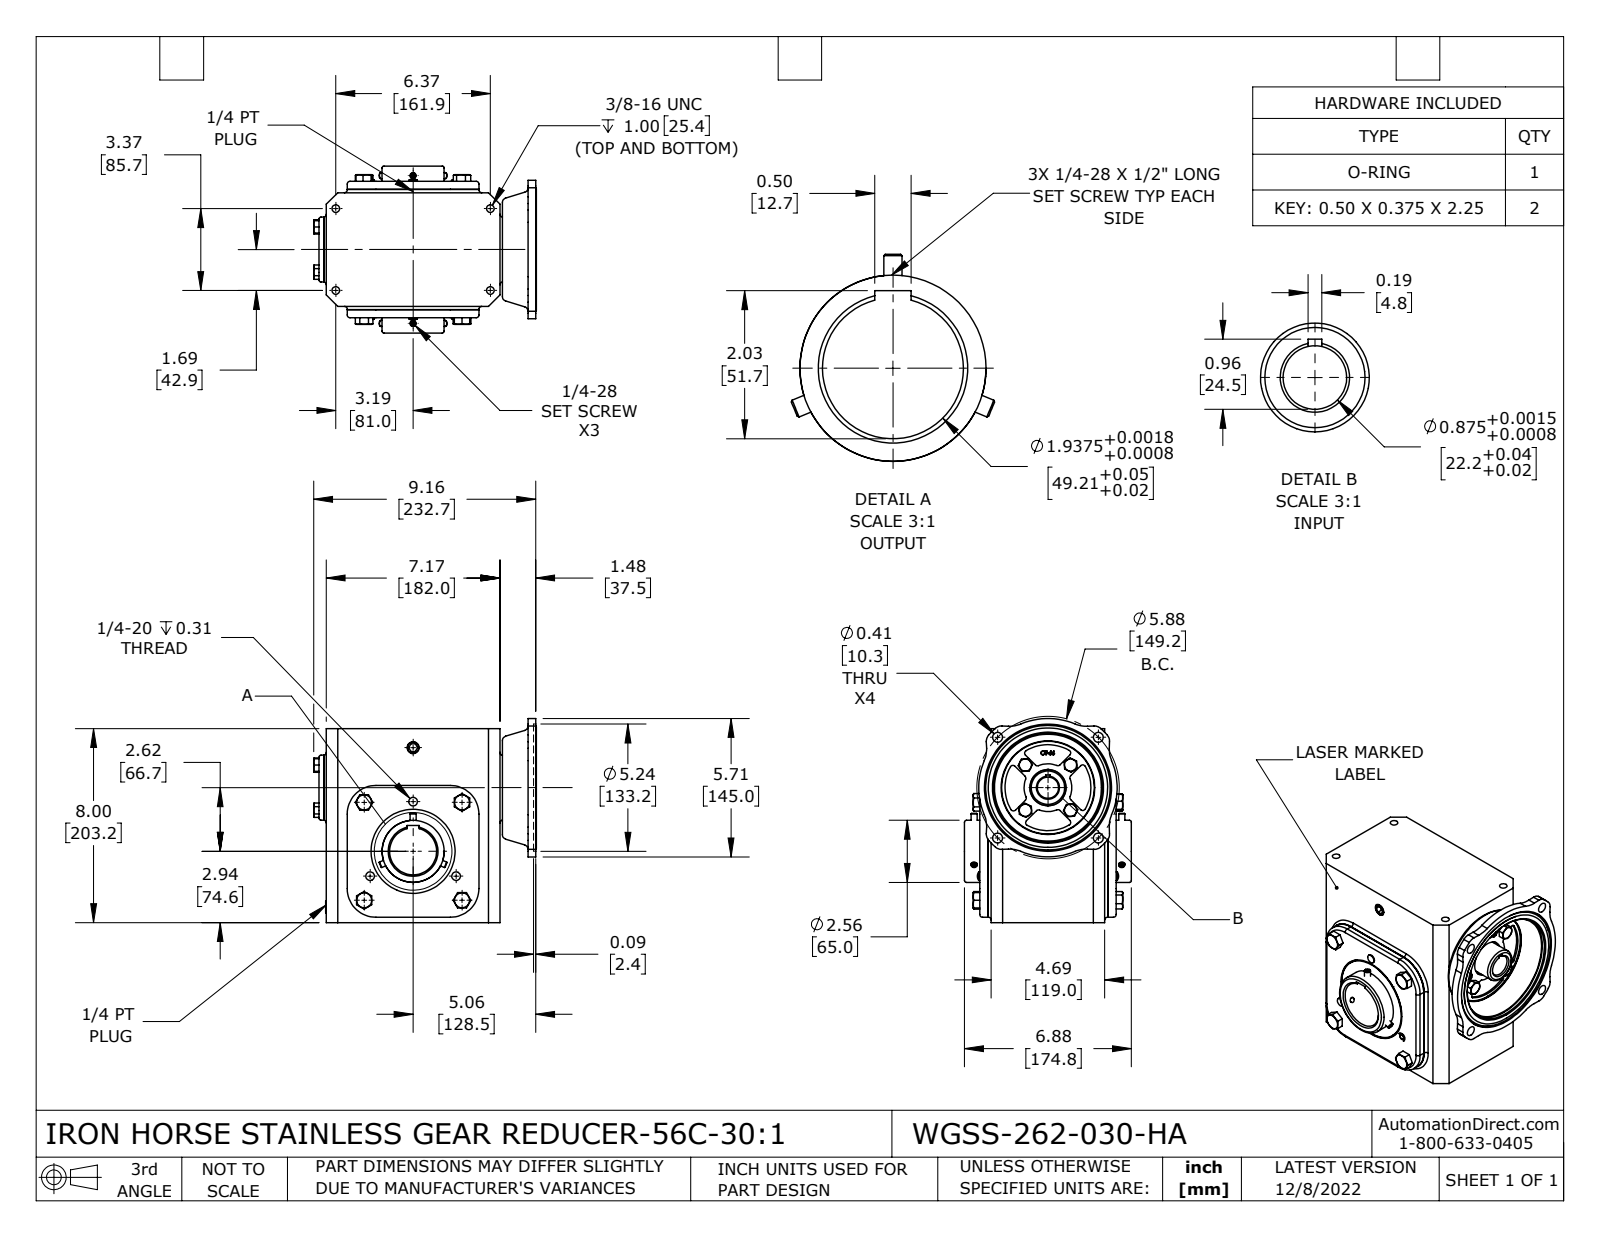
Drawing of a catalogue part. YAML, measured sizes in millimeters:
part_name: "WGSS-262-030-HA"
step_written_by: "SolidWorks 2021 (CONFIG_CONTROL_DESIGN)"
units: millimeters
bodies: {solids: 45, faces: 1776, planar: 625, cylindrical: 516, other: 635}
overall_size: [233.3, 213.8, 174.8]
volume: 1996000
surface_area: 680600
round_holes:
  - {diameter: 5.4, count: 6}
  - {diameter: 6.8, count: 4}
  - {diameter: 8, count: 4}
  - {diameter: 8.5, count: 4}
  - {diameter: 9, count: 4}
  - {diameter: 10.3, count: 4}
  - {diameter: 11, count: 4}
  - {diameter: 5.1, count: 3}
  - {diameter: 2, count: 2}
  - {diameter: 22.2, count: 1}
  - {diameter: 23.9, count: 1}
  - {diameter: 28, count: 1}
round_bosses_or_shafts:
  - {diameter: 6.4, count: 6}
  - {diameter: 18, count: 4}
  - {diameter: 10, count: 4}
  - {diameter: 8, count: 4}
  - {diameter: 9, count: 3}
  - {diameter: 5.2, count: 3}
  - {diameter: 125, count: 1}
  - {diameter: 112, count: 1}
partial_cylinders:
  - {radius: 3, count: 40}
  - {radius: 10, count: 12}
  - {radius: 30, count: 12}
  - {radius: 1, count: 8}
  - {radius: 5, count: 8}
  - {radius: 2, count: 6}
  - {radius: 6, count: 4}
  - {radius: 0.5, count: 2}
face_to_face_distances: [5, 8.5, 126, 17, 198.2, 12, 131, 114, 3.5, 177]
hole_center_spacings: [81.8, 33.5, 41.1, 47.4, 72.5, 74.6, 88, 102.5]
